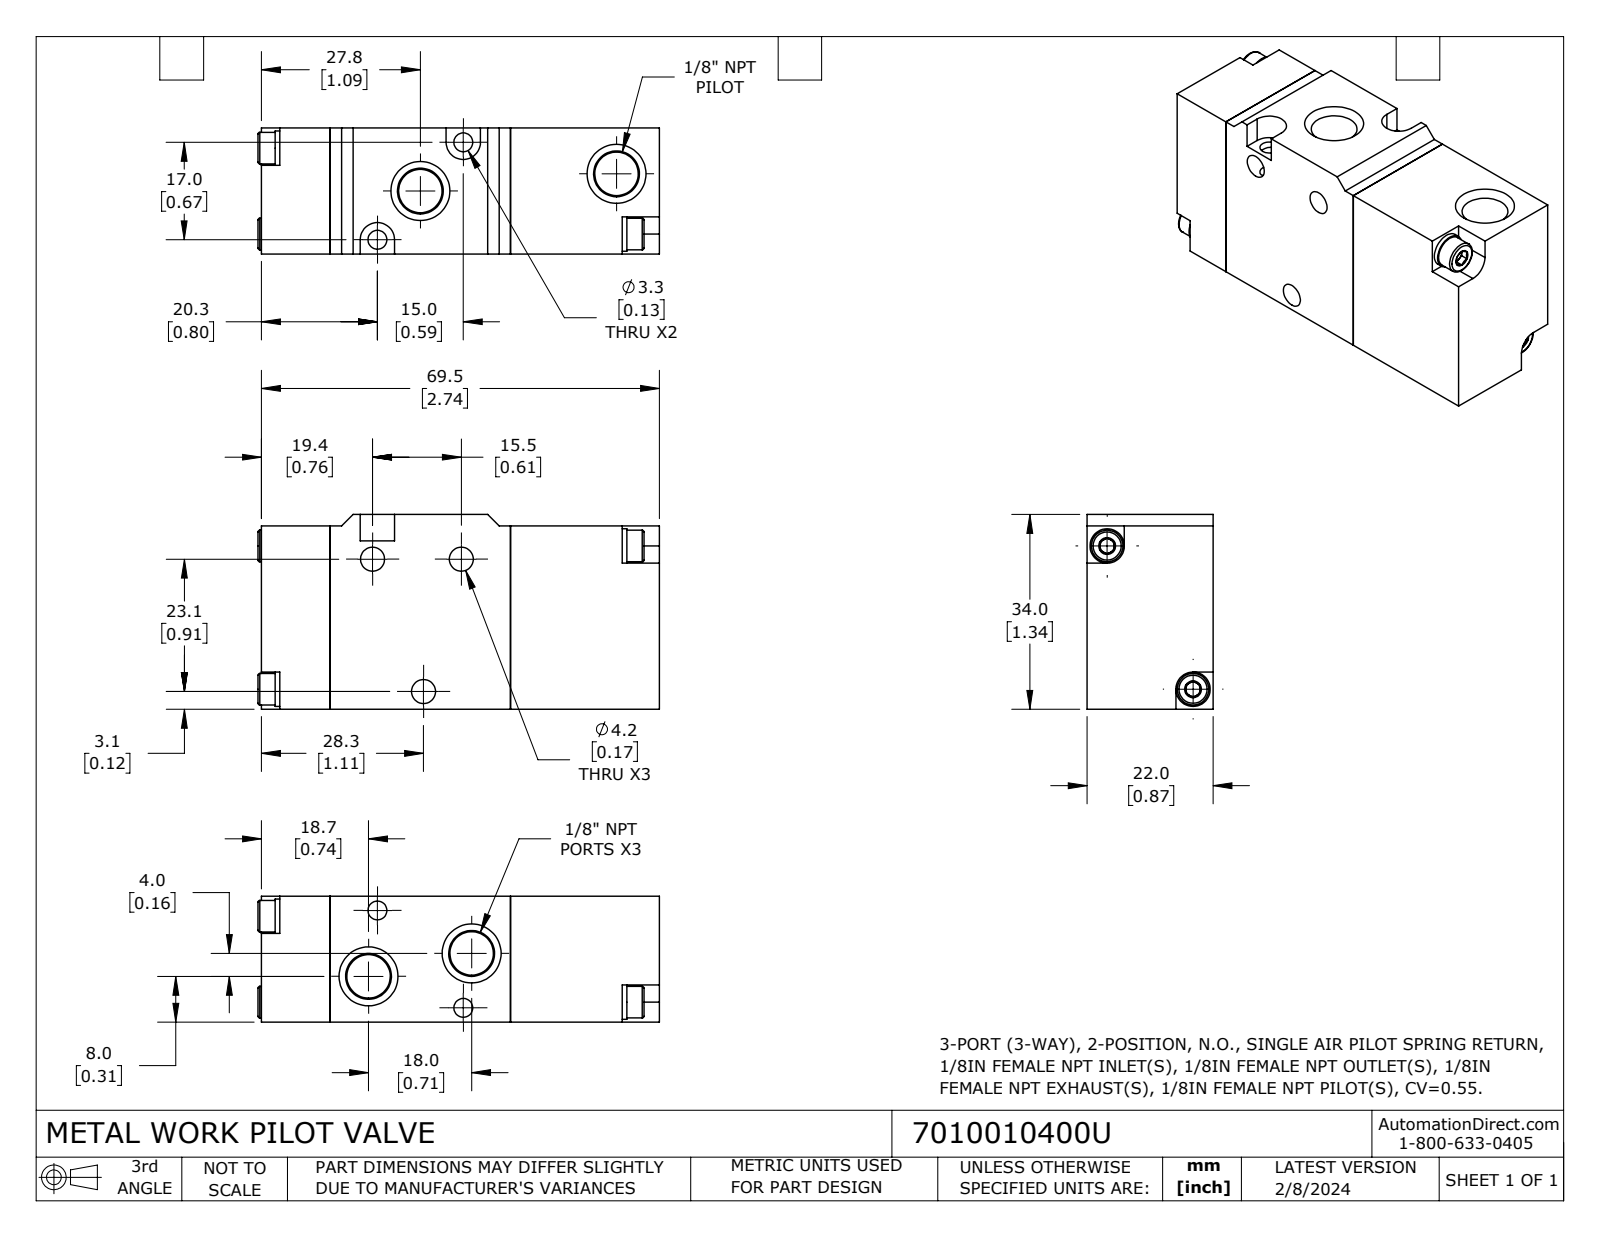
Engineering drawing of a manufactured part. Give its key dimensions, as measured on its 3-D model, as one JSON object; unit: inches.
{"part_name": "7010010400U", "step_written_by": "SolidWorks 2023 (CONFIG_CONTROL_DESIGN)", "units": "inches", "bodies": {"solids": 11, "faces": 236, "planar": 112, "cylindrical": 52, "other": 72}, "overall_size": [2.76, 1.339, 0.866], "volume_in3": 2.85, "surface_area_in2": 23.26, "round_holes": [[0.118, 4], [0.165, 3], [0.13, 2]], "round_bosses_or_shafts": [[0.236, 4], [0.217, 4]], "partial_cylinders_radius": [[0.118, 2]], "face_to_face_distances": [0.866, 1.24, 1.26, 0.472, 1.713, 2.736, 2.264, 1.024, 0.079, 1.339], "hole_center_spacings": [0.591, 0.984, 1.148, 0.61, 0.893, 0.946, 0.975]}
